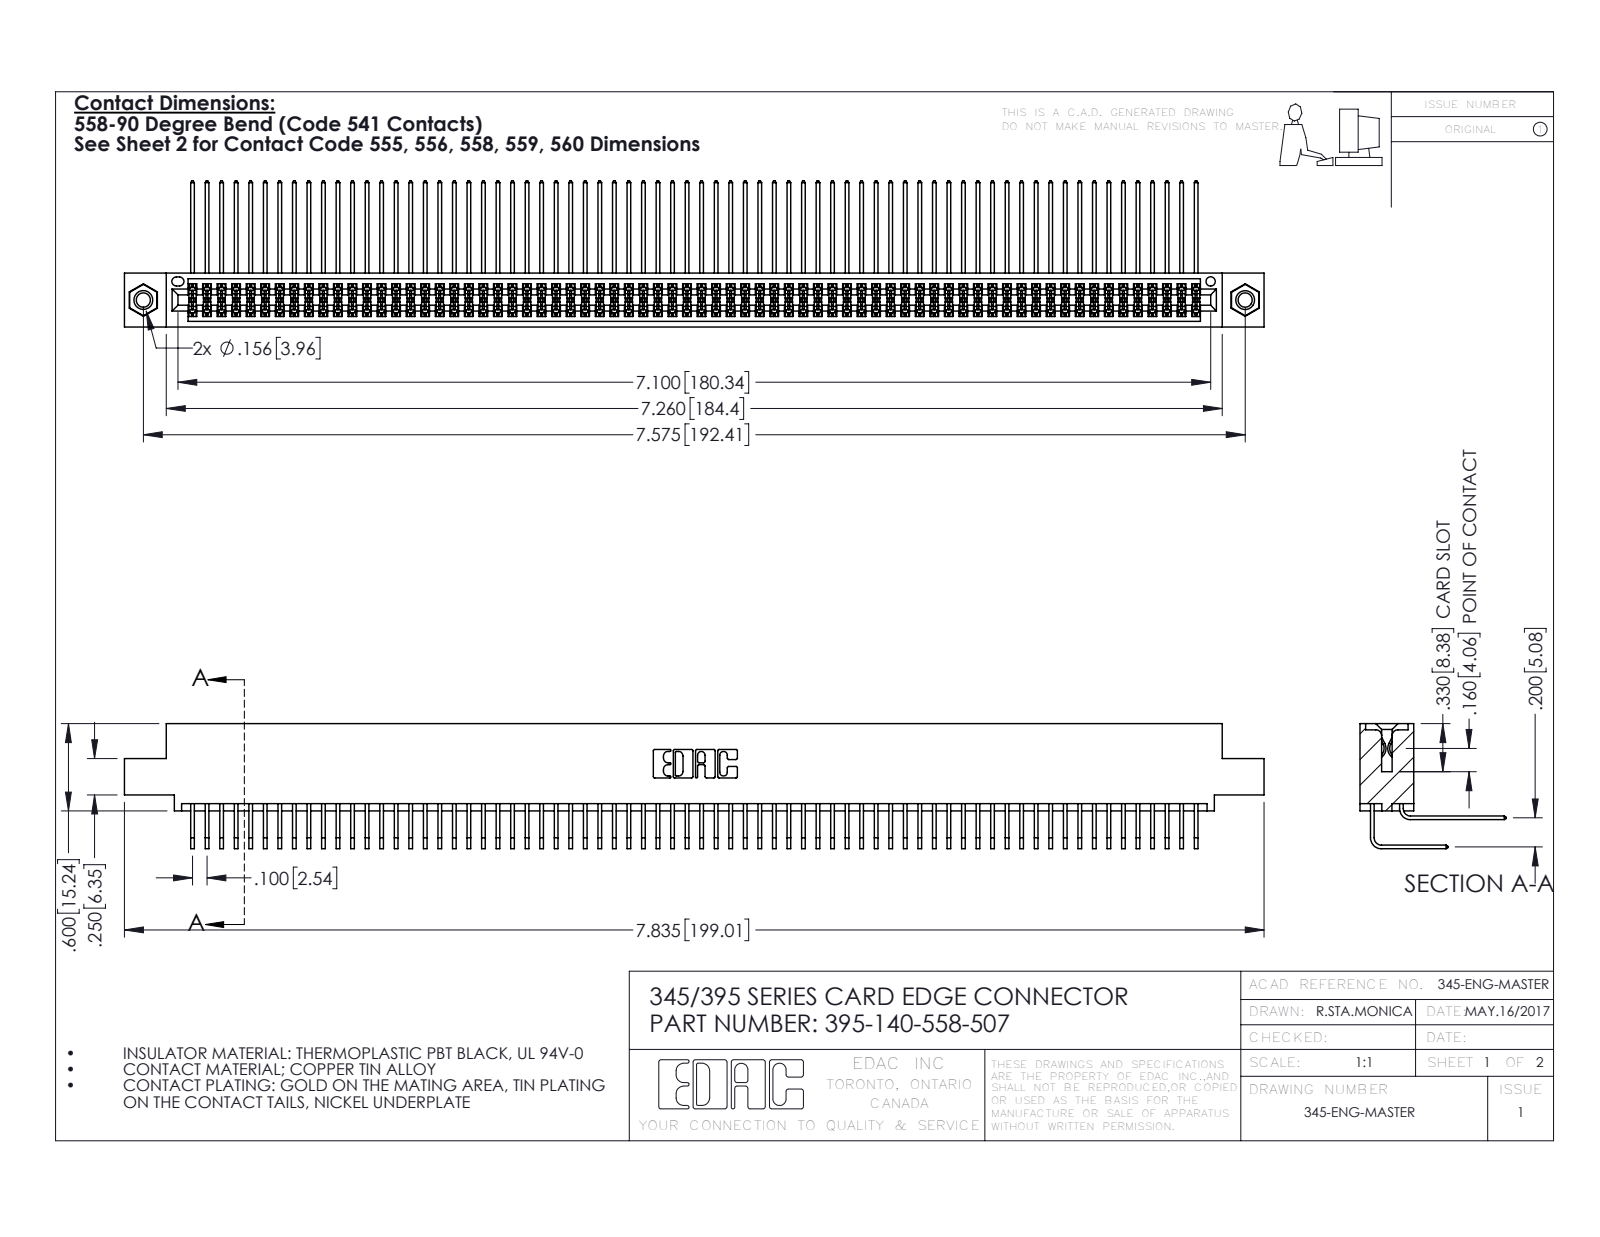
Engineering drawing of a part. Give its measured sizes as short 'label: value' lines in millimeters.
name: 395-140-558-507; 345 Part_0.110 Offset - 0.156 Dia-TI; 345-292-001_558 559 Tail - 1; 345-250-001_345-250-005-103 (+1 more)
written by: SolidWorks 2016 (CONFIG_CONTROL_DESIGN)
unit: mm
bodies: 143 solids, 7470 faces (5016 planar, 2438 cylindrical, 16 other)
size: 199 × 25.5 × 21.8
volume: 20 320 mm³; area: 34 480 mm²
holes: 2× ⌀2.5, 2× ⌀3.2, 2× ⌀4, 1× ⌀1.6
bosses: 2× ⌀3.9
rounds: 279× R0.2, 22× R0.3, 6× R0.2, 6× R0.8, 3× R0.7, 2× R0.4, 2× R0.5, 2× R0.6
face distances: 1.8, 7.6, 5.1, 9.4, 2.5, 6.9, 0.6, 5.7, 0.6, 4.4
hole spacings: 6.9, 186.4, 192.4
